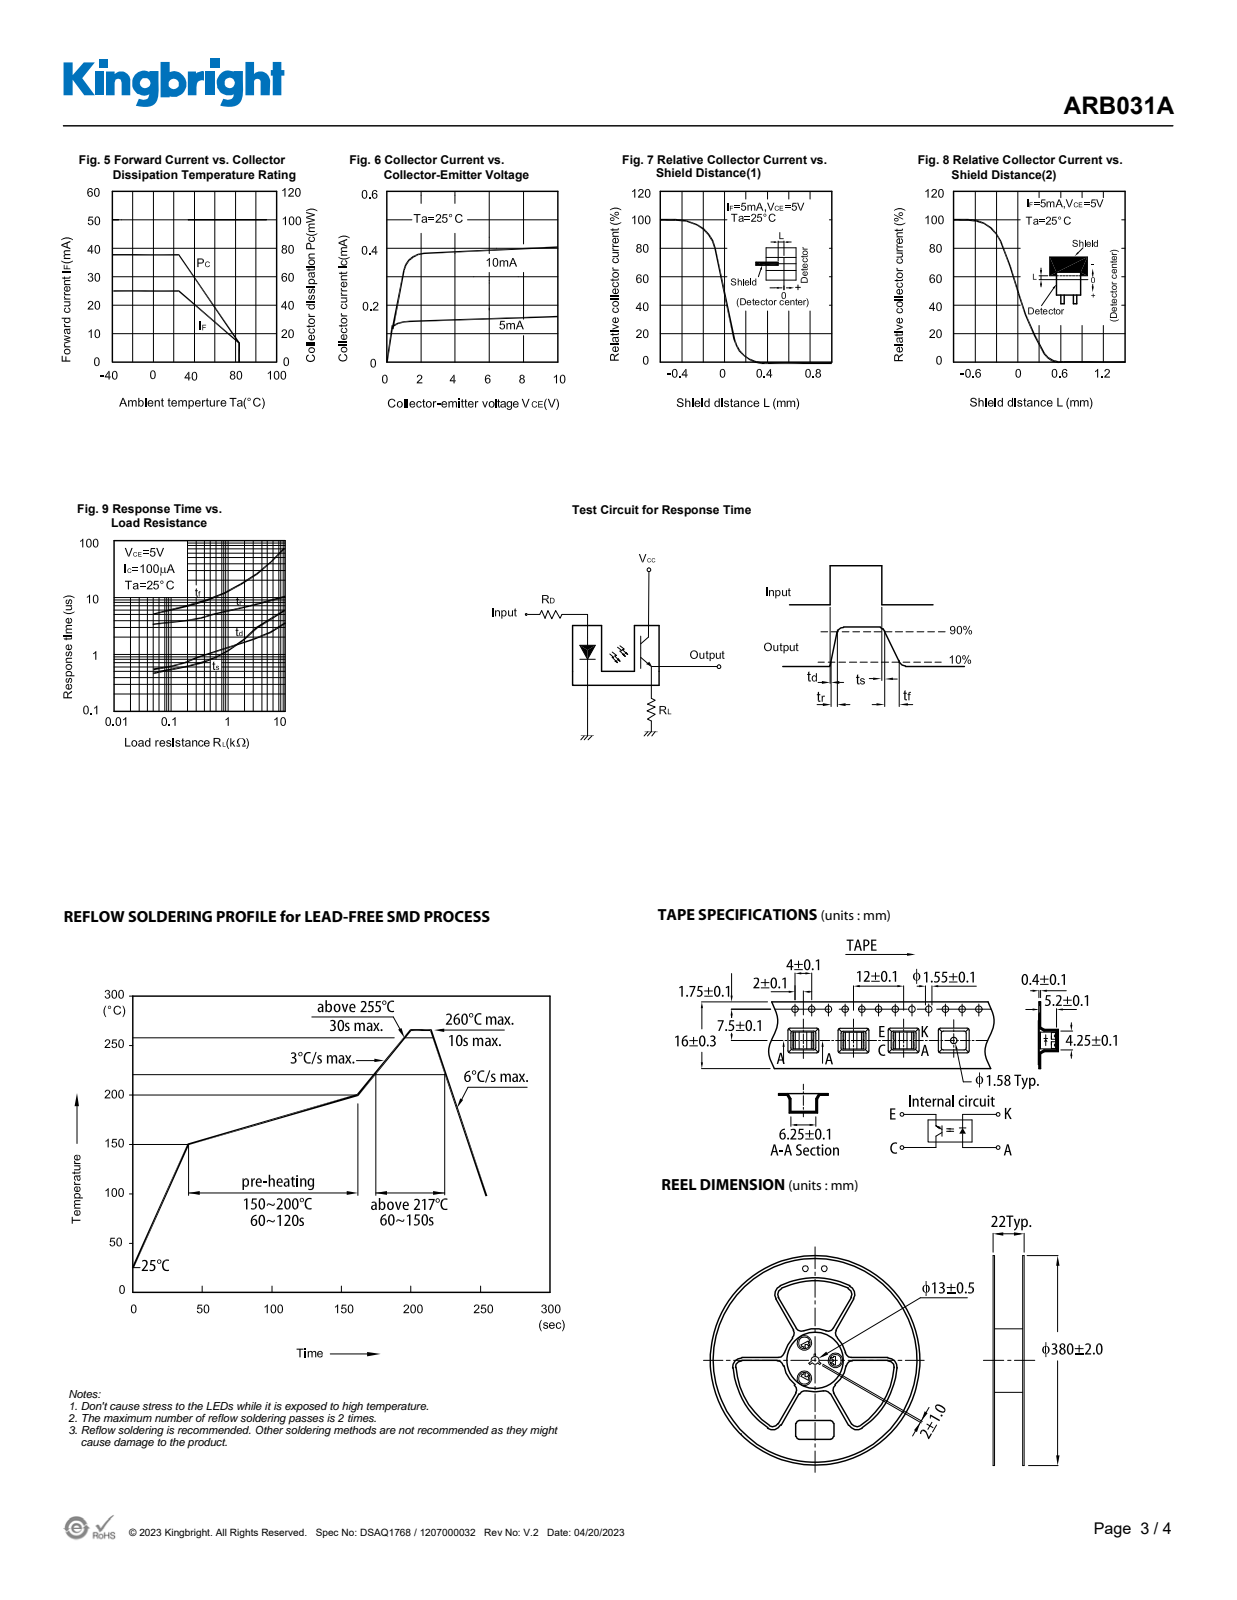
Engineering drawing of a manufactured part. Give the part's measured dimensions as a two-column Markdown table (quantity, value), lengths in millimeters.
| quantity | value |
| --- | --- |
| part name | ARB031A |
| STEP written by | SolidWorks 2014 (AUTOMOTIVE_DESIGN) |
| units | millimeters |
| bodies | 13 solids, 128 faces (104 planar, 24 cylindrical, 0 other) |
| overall size | 5.9 × 5 × 4 |
| volume | 67 mm³ |
| surface area | 189 mm² |
| partial cylindrical surfaces (radius × count) | 0.2 × 2, 0.3 × 2 |
| main face-to-face distances | 1.45, 4.35, 5.8, 4, 1.5, 5, 5.4, 3.5, 2.9, 0.5 |
